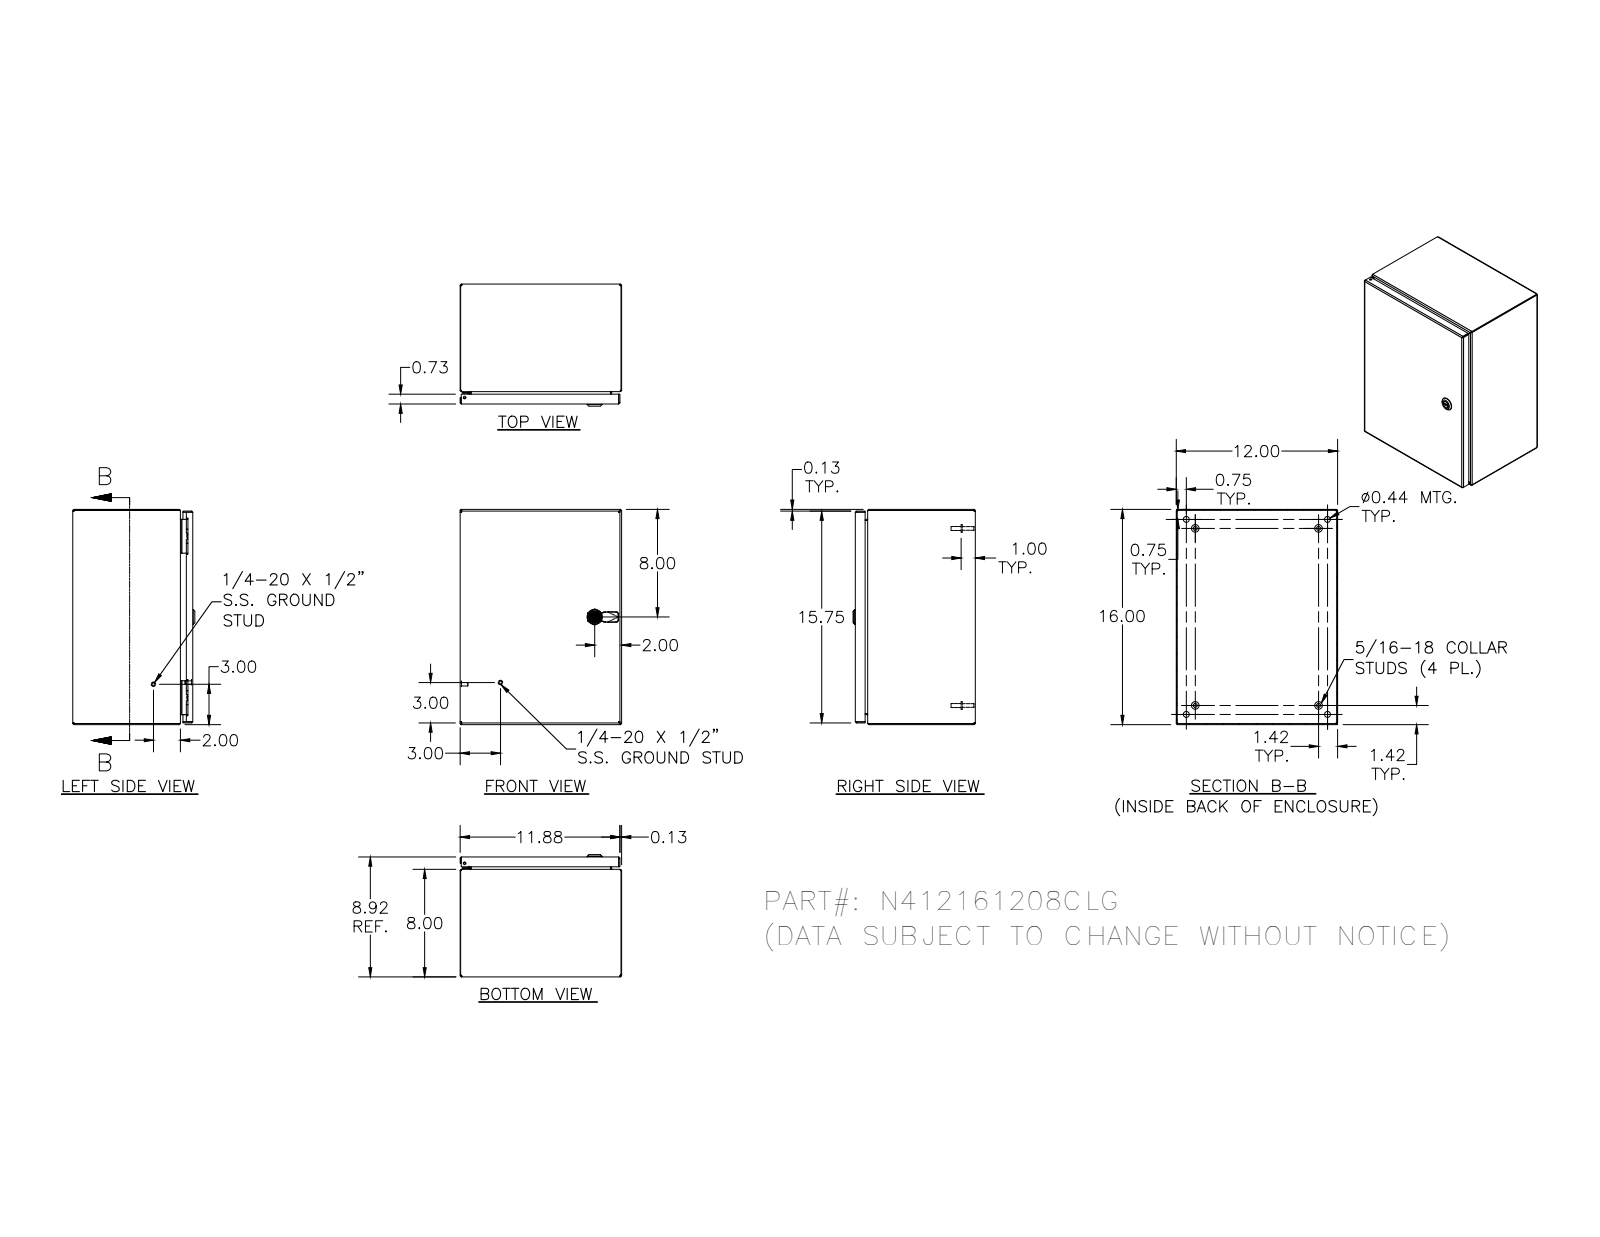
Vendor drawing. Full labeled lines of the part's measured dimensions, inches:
Part name (STEP PRODUCT): N412161208CLG
STEP written by: SolidWorks 2018 (AUTOMOTIVE_DESIGN)
Units: inches
Bodies: 33 solids, 1449 faces (530 planar, 547 cylindrical, 372 other)
Overall size (bounding box): 16 × 12 × 9.075
Volume: 70.47 in³ · Surface area: 1 920 in²
Round holes (diameter × count): ⌀0.188 ×5, ⌀0.093 ×4, ⌀0.152 ×4, ⌀0.167 ×4, ⌀0.172 ×4, ⌀0.437 ×4, ⌀0.156 ×2, ⌀0.187 ×1, ⌀0.197 ×1, ⌀0.315 ×1, ⌀0.394 ×1, ⌀0.402 ×1
Round bosses / shafts (diameter × count): ⌀0.25 ×10, ⌀0.563 ×4, ⌀0.36 ×4, ⌀0.32 ×4, ⌀0.3 ×4, ⌀0.275 ×4, ⌀0.256 ×4, ⌀0.164 ×4
Partial cylindrical surfaces — rounded edges, fillets, slot ends (radius × count): R0.012 ×30, R0.031 ×30, R0.05 ×26, R0.105 ×20, R0.016 ×18, R0.125 ×16, R0.02 ×13, R0.032 ×8
Main face-to-face distances: 0.074, 8.843, 0.074, 8.769, 8.917, 11.926, 12, 11.852, 11.926, 15.926
Hole centre spacings: 12, 0.66, 0.656, 1.307, 1.965, 0.5, 0.984, 1.311
